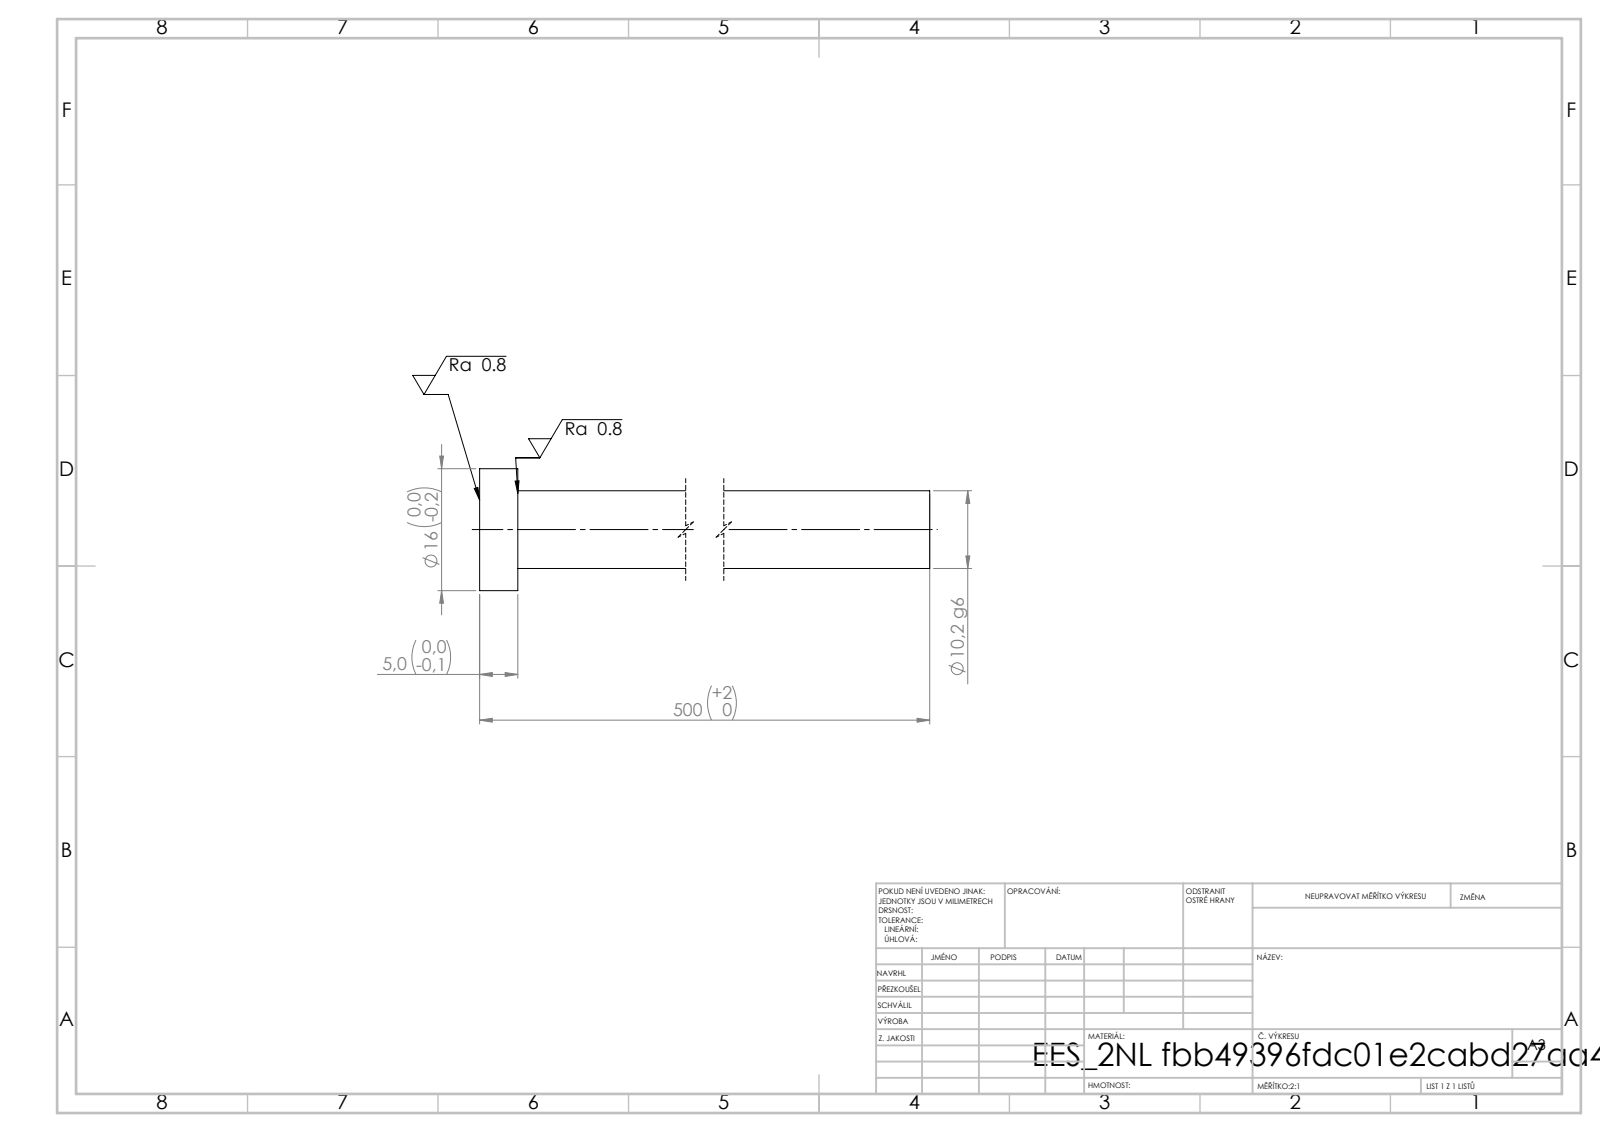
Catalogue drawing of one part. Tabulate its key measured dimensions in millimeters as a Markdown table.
| quantity | value |
| --- | --- |
| STEP written by | SolidWorks 2019 (CONFIG_CONTROL_DESIGN) |
| units | millimeters |
| bodies | 1 solid, 7 faces (3 planar, 4 cylindrical, 0 other) |
| overall size | 500 × 16 × 16 |
| volume | 41 453 mm³ |
| surface area | 16 515 mm² |
| round bosses / shafts (diameter × count) | 16 × 1, 10.2 × 1 |
| main face-to-face distances | 5, 500, 495 |
